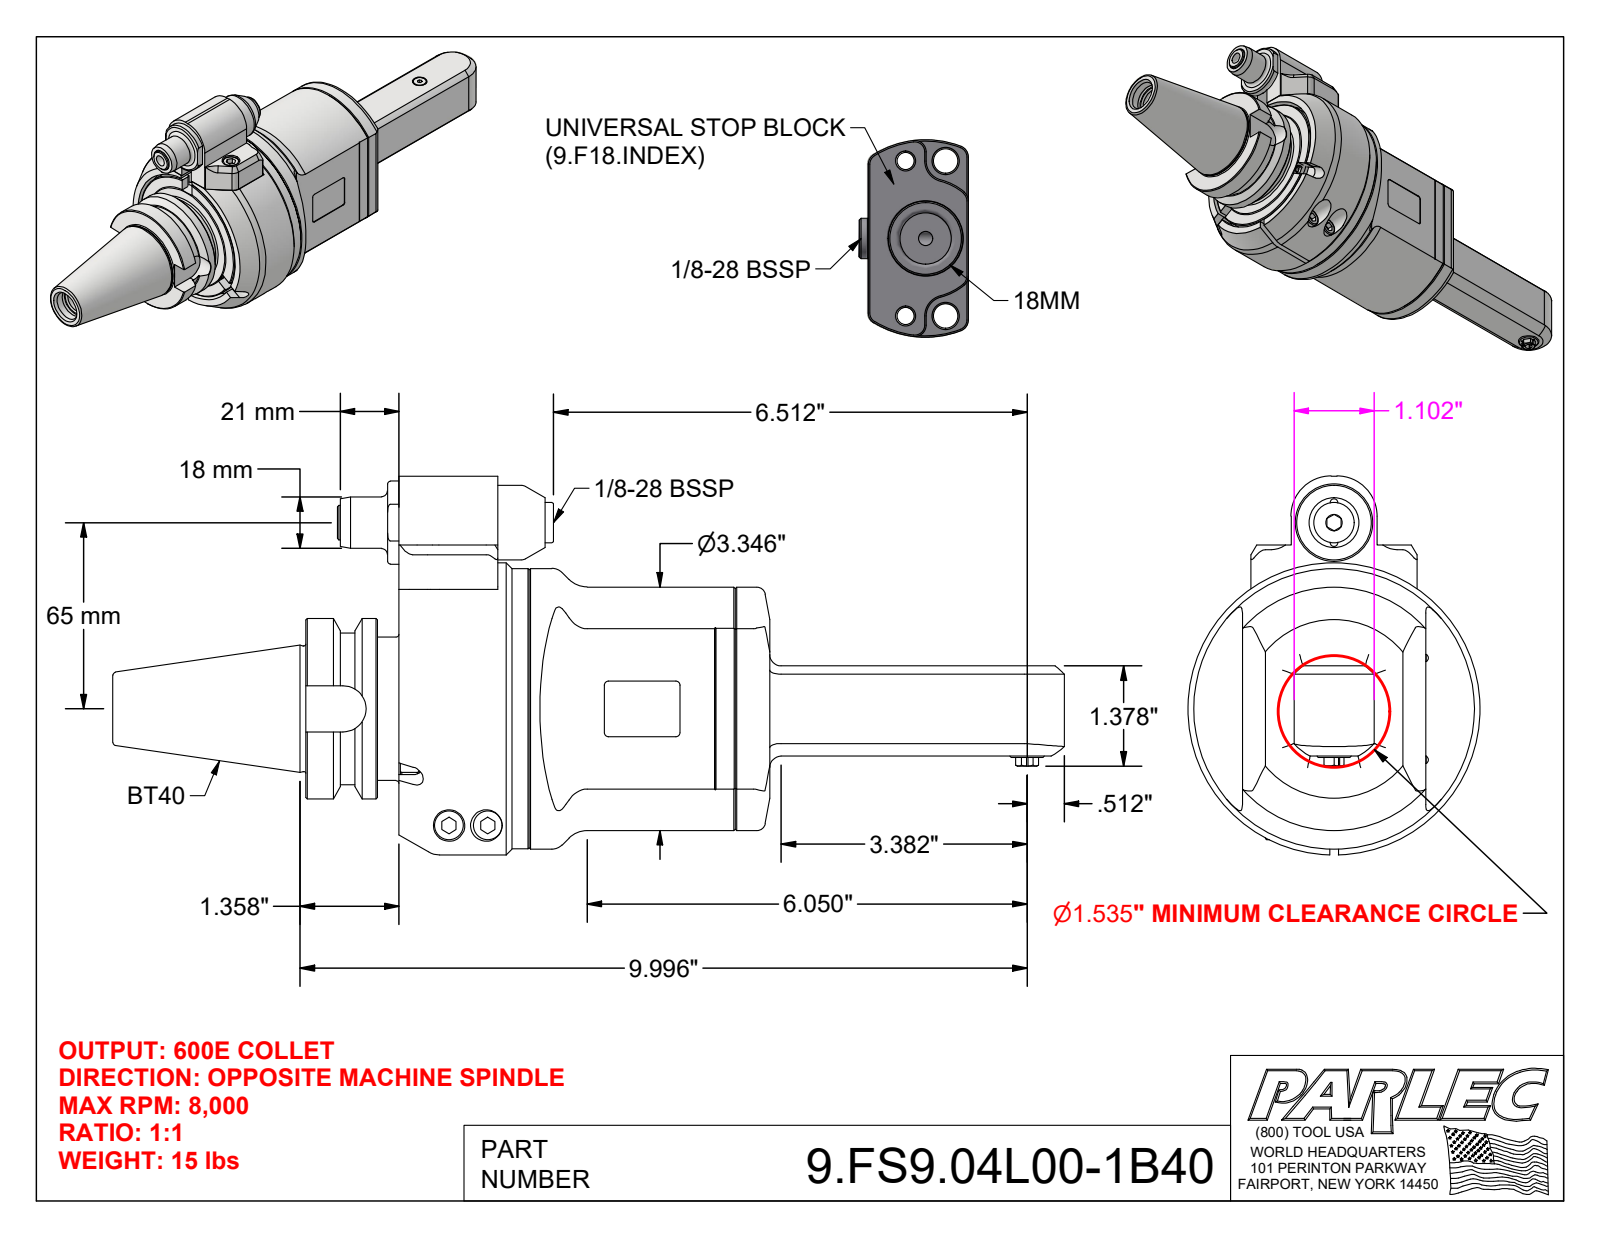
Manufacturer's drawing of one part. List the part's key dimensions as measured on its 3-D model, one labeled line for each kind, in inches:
Part name (STEP PRODUCT): 9.FS9.04L00-1B40; 9_FS9_04L00; 9_GA1_346_2 (Type 1, BT40, 65mm)
STEP written by: Autodesk Inventor 2022 (AUTOMOTIVE_DESIGN)
Units: inches
Bodies: 5 solids, 488 faces (240 planar, 127 cylindrical, 121 other)
Overall size (bounding box): 13.082 × 5.206 × 4.016
Volume: 63.19 in³ · Surface area: 231.4 in²
Round holes (diameter × count): ⌀0.102 ×2, ⌀0.118 ×2, ⌀0.165 ×2, ⌀0.197 ×2, ⌀0.335 ×2, ⌀0.409 ×2, ⌀0.433 ×2, ⌀0.098 ×1, ⌀0.157 ×1, ⌀0.256 ×1, ⌀0.276 ×1, ⌀0.472 ×1
Round bosses / shafts (diameter × count): ⌀0.394 ×4, ⌀0.236 ×4, ⌀0.315 ×3, ⌀0.709 ×2, ⌀0.098 ×2, ⌀4.016 ×1, ⌀3.858 ×1, ⌀3.85 ×1
Partial cylindrical surfaces — rounded edges, fillets, slot ends (radius × count): R0.157 ×10, R0.079 ×8, R0.059 ×4, R0.551 ×3, R0.02 ×2, R0.039 ×2, R0.138 ×2, R0.197 ×2
Main face-to-face distances: 0.709, 0.118, 1.811, 1.555, 0.295, 1.378, 0.157, 1.26, 1.102, 0.02
Hole centre spacings: 0.276, 0.512, 0.551, 1.081, 1.72, 2.283, 2.559, 2.764
